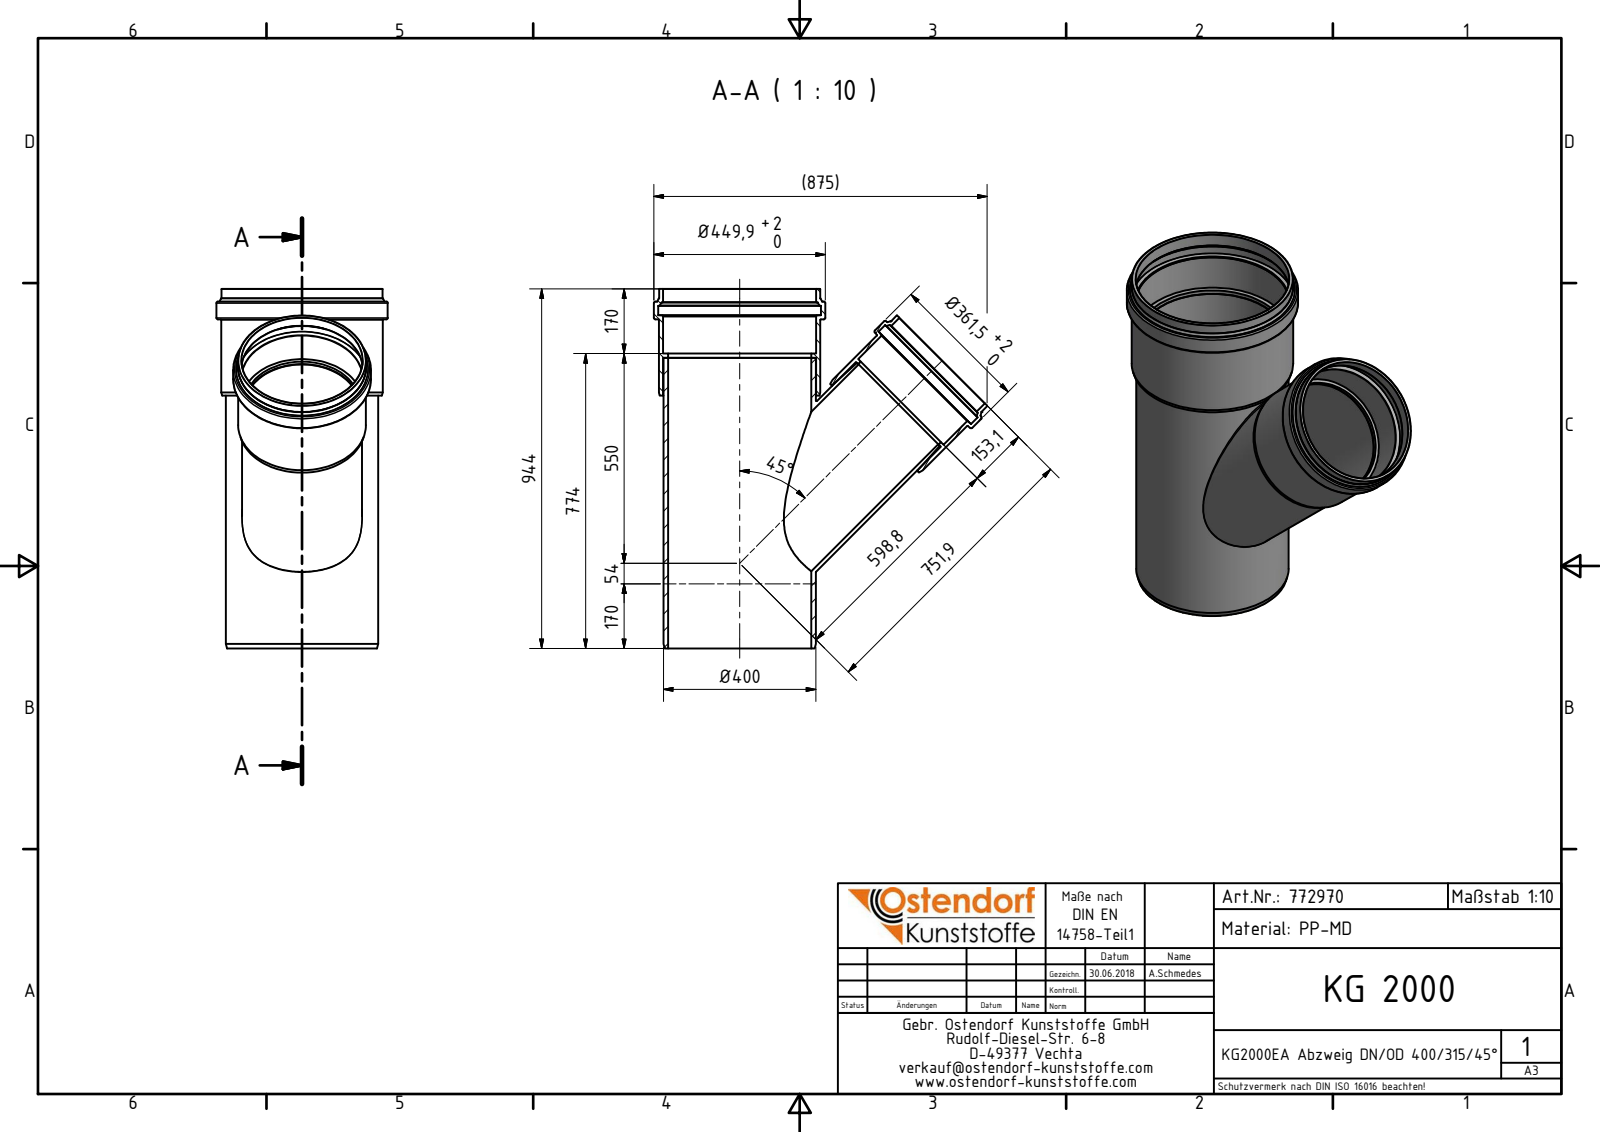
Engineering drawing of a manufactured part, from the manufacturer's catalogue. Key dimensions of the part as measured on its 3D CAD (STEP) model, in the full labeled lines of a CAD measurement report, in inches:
Part name (STEP PRODUCT): 772970 KG2000EA Abzweig DN_OD 400_315_45° Teil 1; 772970 KG2000EA Abzweig DN_OD 400_315_45° Teil 2; 772970 KG2000EA Abzweig DN_OD 400_315_45° Teil 3; 772970 KG2000EA Abzweig DN_OD 400_315_45°
STEP written by: Autodesk Inventor 2016 (AUTOMOTIVE_DESIGN)
Units: inches
Bodies: 3 solids, 80 faces (14 planar, 20 cylindrical, 46 other)
Overall size (bounding box): 37.165 × 34.449 × 17.713
Volume: 1 253 in³ · Surface area: 5 871 in²
Round holes (diameter × count): ⌀11.638 ×1, ⌀11.732 ×1, ⌀12.492 ×1, ⌀12.508 ×1, ⌀13.516 ×1, ⌀14.803 ×1, ⌀15.815 ×1, ⌀15.831 ×1, ⌀16.839 ×1
Round bosses / shafts (diameter × count): ⌀17.713 ×1, ⌀16.689 ×1, ⌀16.656 ×1, ⌀15.748 ×1, ⌀14.232 ×1, ⌀13.224 ×1, ⌀13.209 ×1, ⌀12.402 ×1
Main face-to-face distances: 0.437, 3.894, 4.331, 11.024, 7.13, 6.693, 26.142, 30.035, 30.472, 37.165
